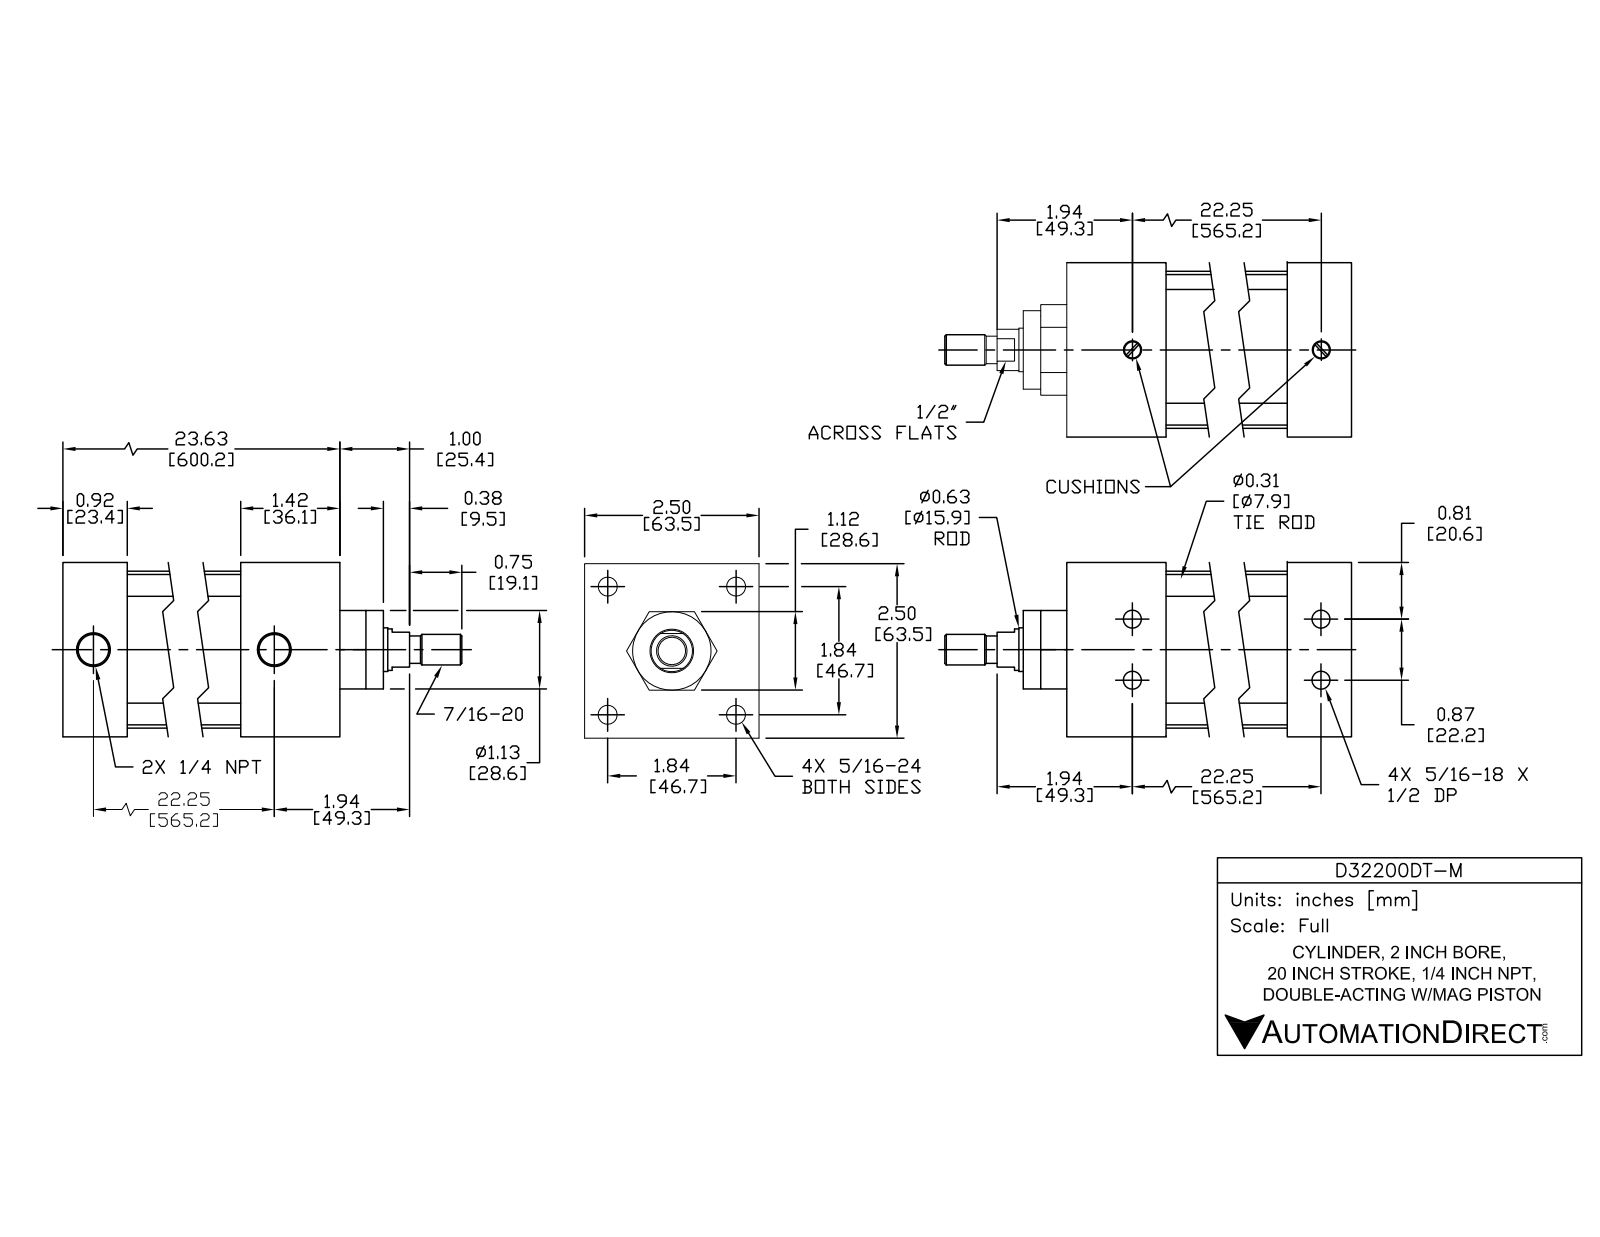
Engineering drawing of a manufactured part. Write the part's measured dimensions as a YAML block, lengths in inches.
part_name: "D32200DT-M PISTON; D32200DT-M BODY; D32200DT-MC"
step_written_by: "SolidWorks 2015 (AUTOMOTIVE_DESIGN)"
units: inches
bodies: {solids: 12, faces: 298, planar: 94, cylindrical: 114, other: 90}
overall_size: [25.371, 2.5, 2.5]
volume: 47.6
surface_area: 500.5
round_holes:
  - {diameter: 0.252, count: 4}
  - {diameter: 0.267, count: 4}
  - {diameter: 0.359, count: 4}
  - {diameter: 0.5, count: 4}
  - {diameter: 0.297, count: 2}
  - {diameter: 0.477, count: 2}
  - {diameter: 0.625, count: 1}
  - {diameter: 0.628, count: 1}
  - {diameter: 2, count: 1}
round_bosses_or_shafts:
  - {diameter: 0.484, count: 4}
  - {diameter: 0.313, count: 4}
  - {diameter: 0.282, count: 4}
  - {diameter: 2.25, count: 1}
  - {diameter: 1.997, count: 1}
  - {diameter: 1.12, count: 1}
  - {diameter: 0.622, count: 1}
  - {diameter: 0.59, count: 1}
partial_cylinders:
  - {radius: 0.25, count: 4}
face_to_face_distances: [2.5, 0.08, 21.201, 23.621, 1.42, 22.201, 22.701, 21.281, 0.92, 1]
hole_center_spacings: [1.307, 1.848, 22.25, 22.245, 0.437, 0.438, 0.875, 2.613]
